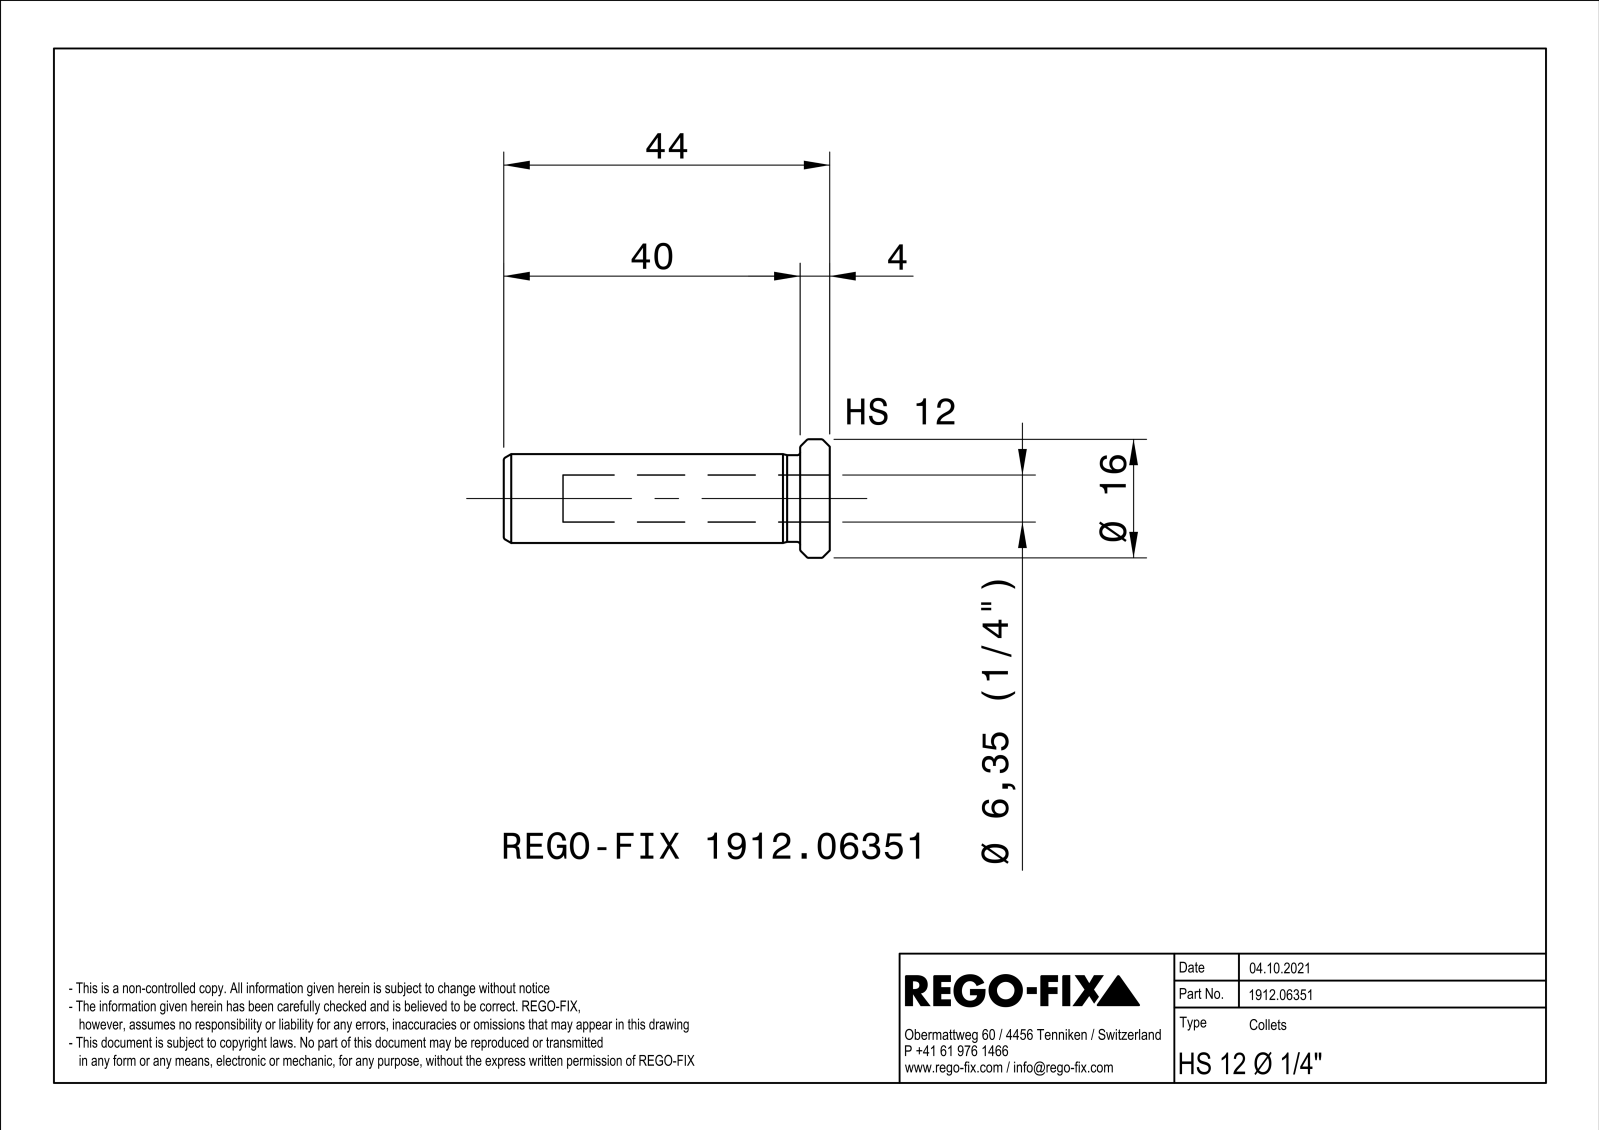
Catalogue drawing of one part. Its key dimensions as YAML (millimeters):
part_name: "NOCUT"
step_written_by: "SIEMENS PLM Software Solid Edge ST10 (AUTOMOTIVE_DESIGN)"
units: millimeters
bodies: {solids: 1, faces: 69, planar: 22, cylindrical: 11, other: 36}
overall_size: [44, 15.98, 15.98]
volume: 3469
surface_area: 3448
round_holes:
  - {diameter: 6.35, count: 1}
  - {diameter: 7.5, count: 1}
round_bosses_or_shafts:
  - {diameter: 16, count: 1}
  - {diameter: 12, count: 1}
  - {diameter: 11.7, count: 1}
face_to_face_distances: [0.8, 44, 4, 40]
